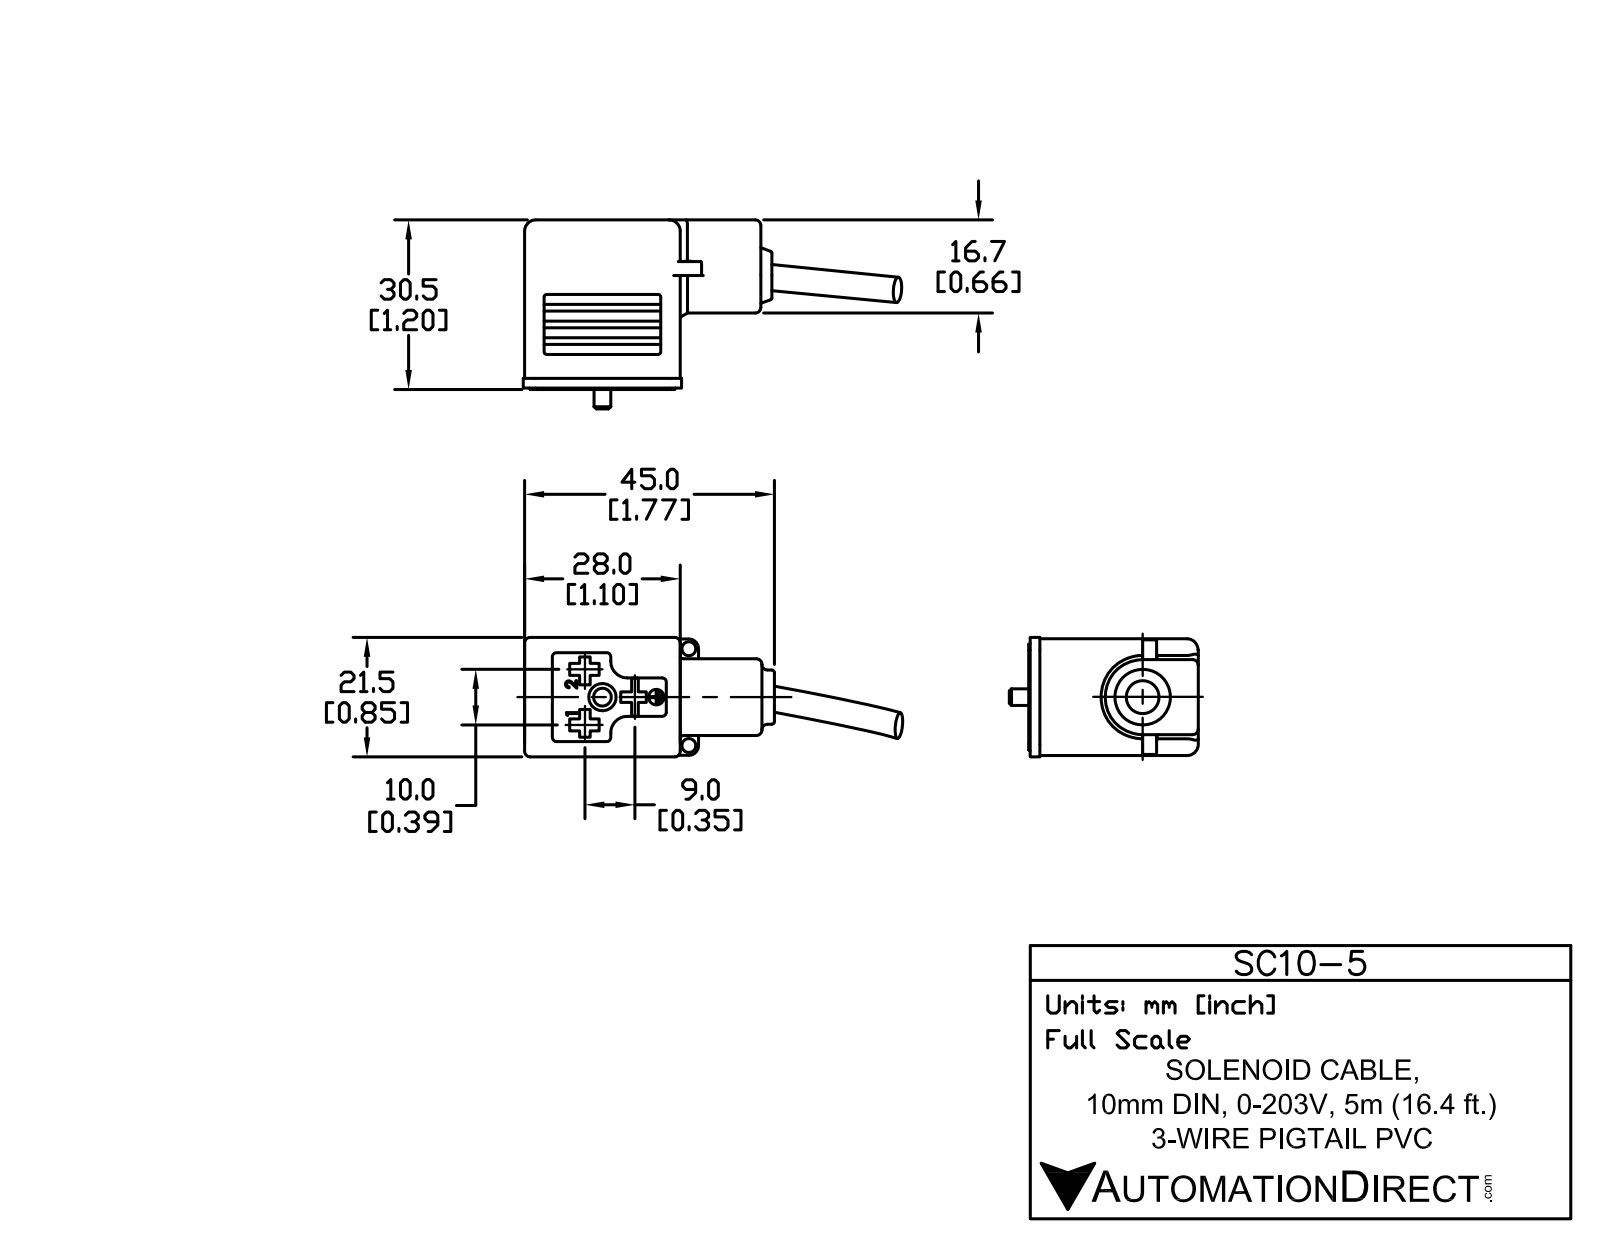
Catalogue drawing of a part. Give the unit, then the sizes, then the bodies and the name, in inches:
Units: inches
Overall size (bounding box): 2.668 × 1.35 × 0.846
Round holes (diameter × count): ⌀0.098 ×2, ⌀0.109 ×1, ⌀0.126 ×1, ⌀0.193 ×1, ⌀0.22 ×1, ⌀0.26 ×1
Round bosses / shafts (diameter × count): ⌀0.384 ×1, ⌀0.256 ×1, ⌀0.108 ×1
Partial cylindrical surfaces — rounded edges, fillets, slot ends (radius × count): R0.039 ×19, R0.03 ×6, R0.069 ×2, R0.118 ×2, R0.272 ×1
Main face-to-face distances: 0.823, 1.181, 1.079, 0.14, 1.102, 0.079, 0.683, 1.1, 1.179, 0.543
Hole centre spacings: 0.413, 0.702, 0.382, 0.685
Volume: 1.213 in³ · Surface area: 10.52 in²
Bodies: 2 solids, 202 faces (130 planar, 45 cylindrical, 27 other)
Part name (STEP PRODUCT): SC10-5
STEP written by: SolidWorks 2011 (AUTOMOTIVE_DESIGN)
